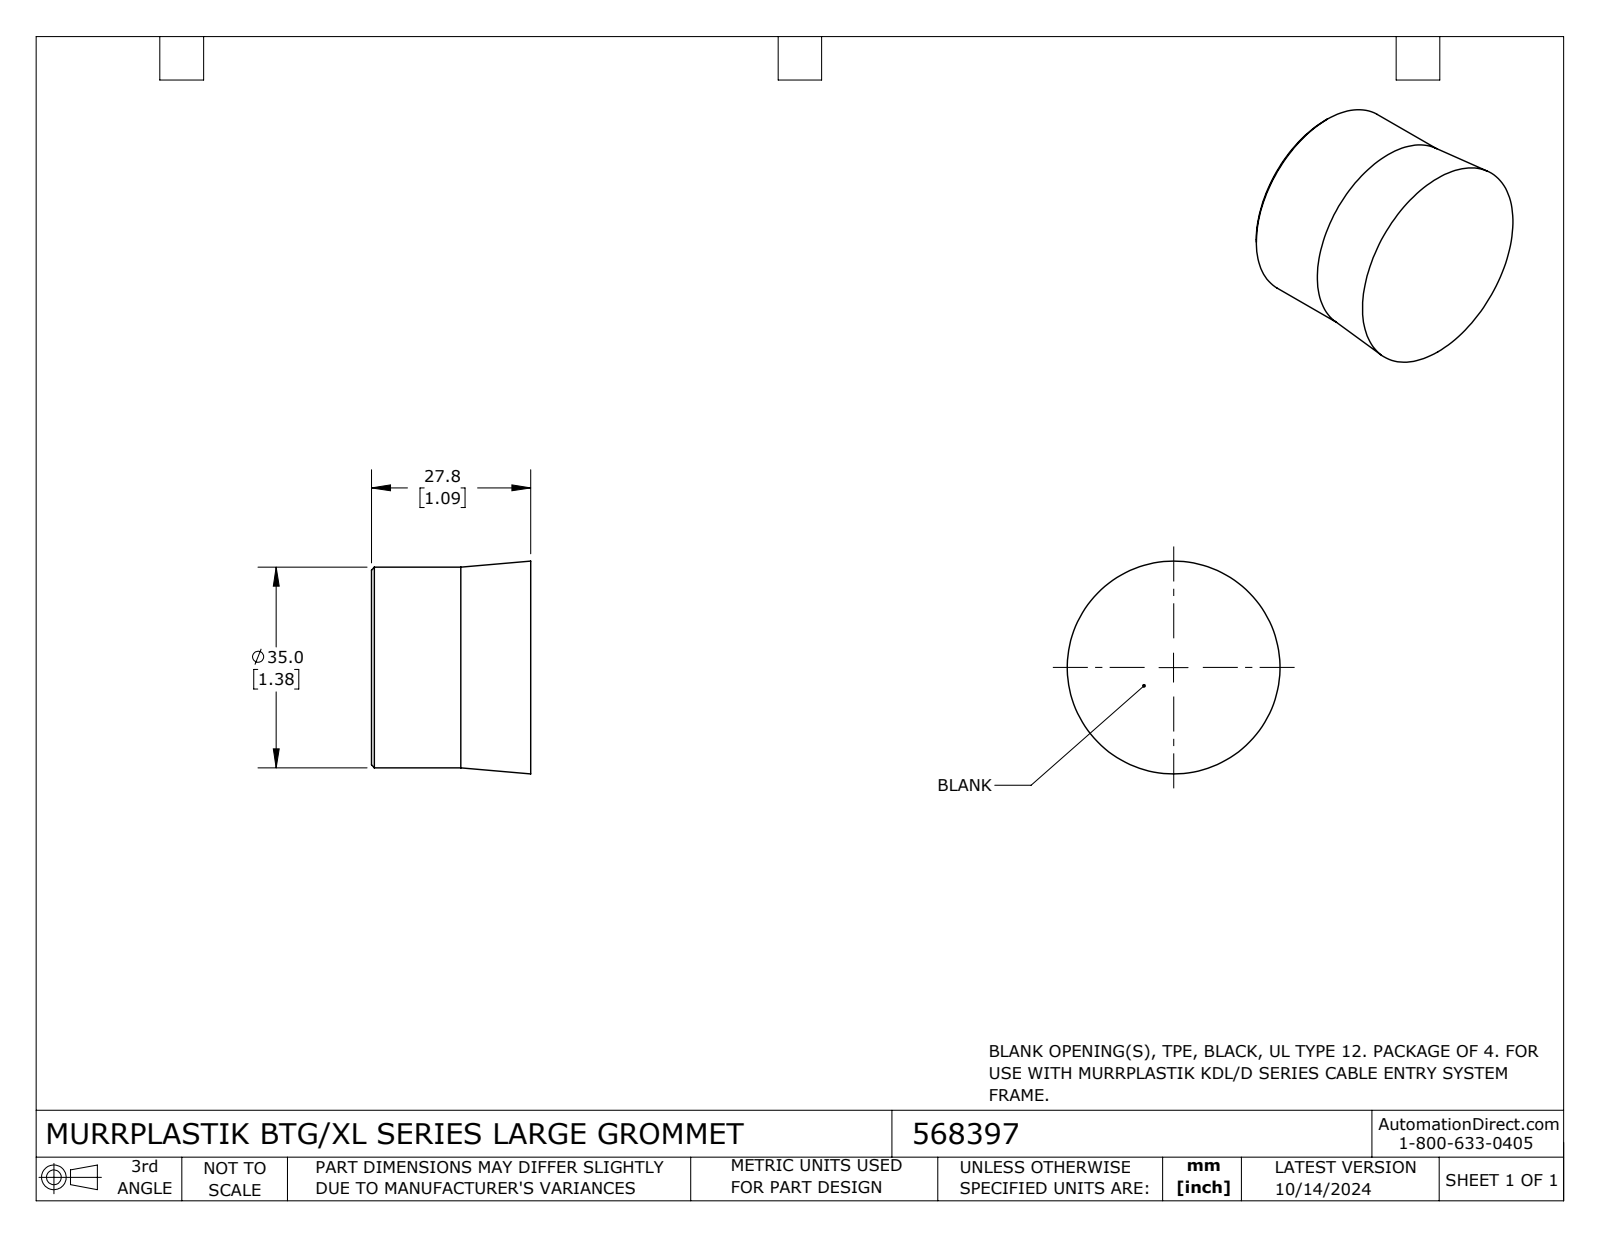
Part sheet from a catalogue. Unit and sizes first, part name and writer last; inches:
Units: inches
Overall size (bounding box): 1.462 × 1.462 × 1.094
Round bosses / shafts (diameter × count): ⌀1.378 ×1
Main face-to-face distances: 1.094
Volume: 1.676 in³ · Surface area: 7.93 in²
Bodies: 1 solid, 8 faces (2 planar, 2 cylindrical, 4 other)
Part name (STEP PRODUCT): 568397
STEP written by: SolidWorks 2023 (CONFIG_CONTROL_DESIGN)
